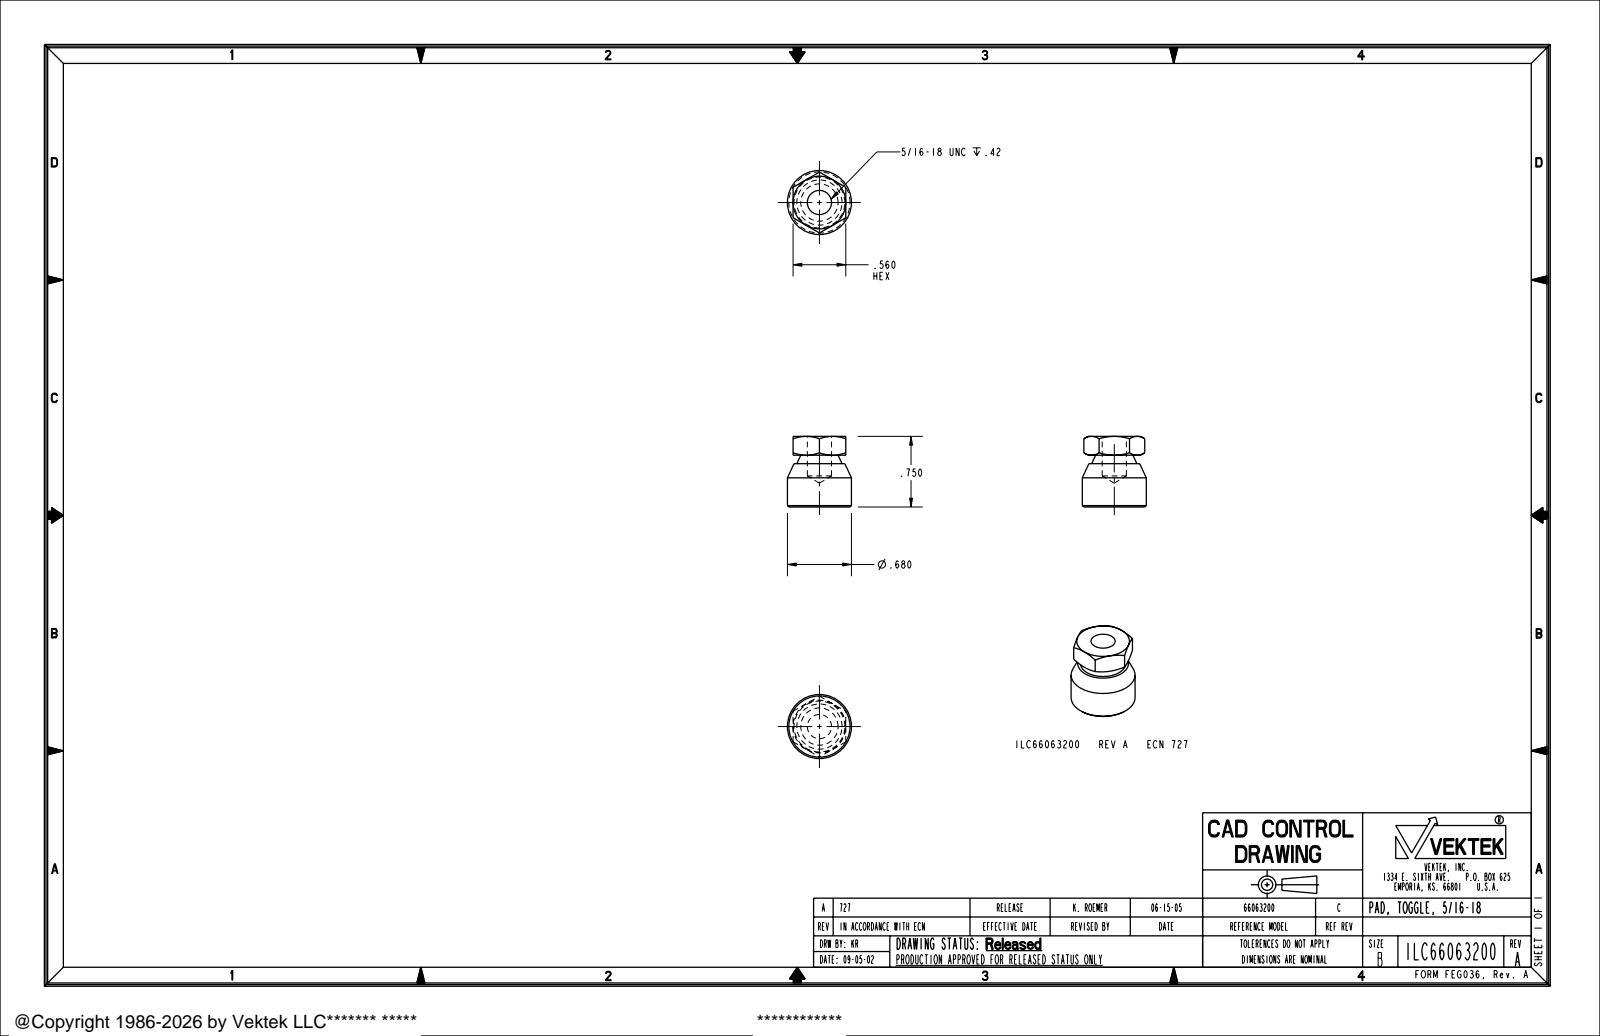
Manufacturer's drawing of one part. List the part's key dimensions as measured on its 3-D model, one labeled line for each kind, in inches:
Part name (STEP PRODUCT): ILC66063200
STEP written by: PRO/ENGINEER BY PARAMETRIC TECHNOLOGY CORPORATION, 2004290 (AUTOMOTIVE_DESIGN_CC2)
Units: inches
Bodies: 1 solid, 34 faces (10 planar, 4 cylindrical, 20 other)
Overall size (bounding box): 0.75 × 0.68 × 0.68
Volume: 0.201 in³ · Surface area: 2.639 in²
Round holes (diameter × count): ⌀0.257 ×1
Round bosses / shafts (diameter × count): ⌀0.68 ×1
Main face-to-face distances: 0.75, 0.56, 0.55, 0.2, 0.46, 0.09, 0.29
